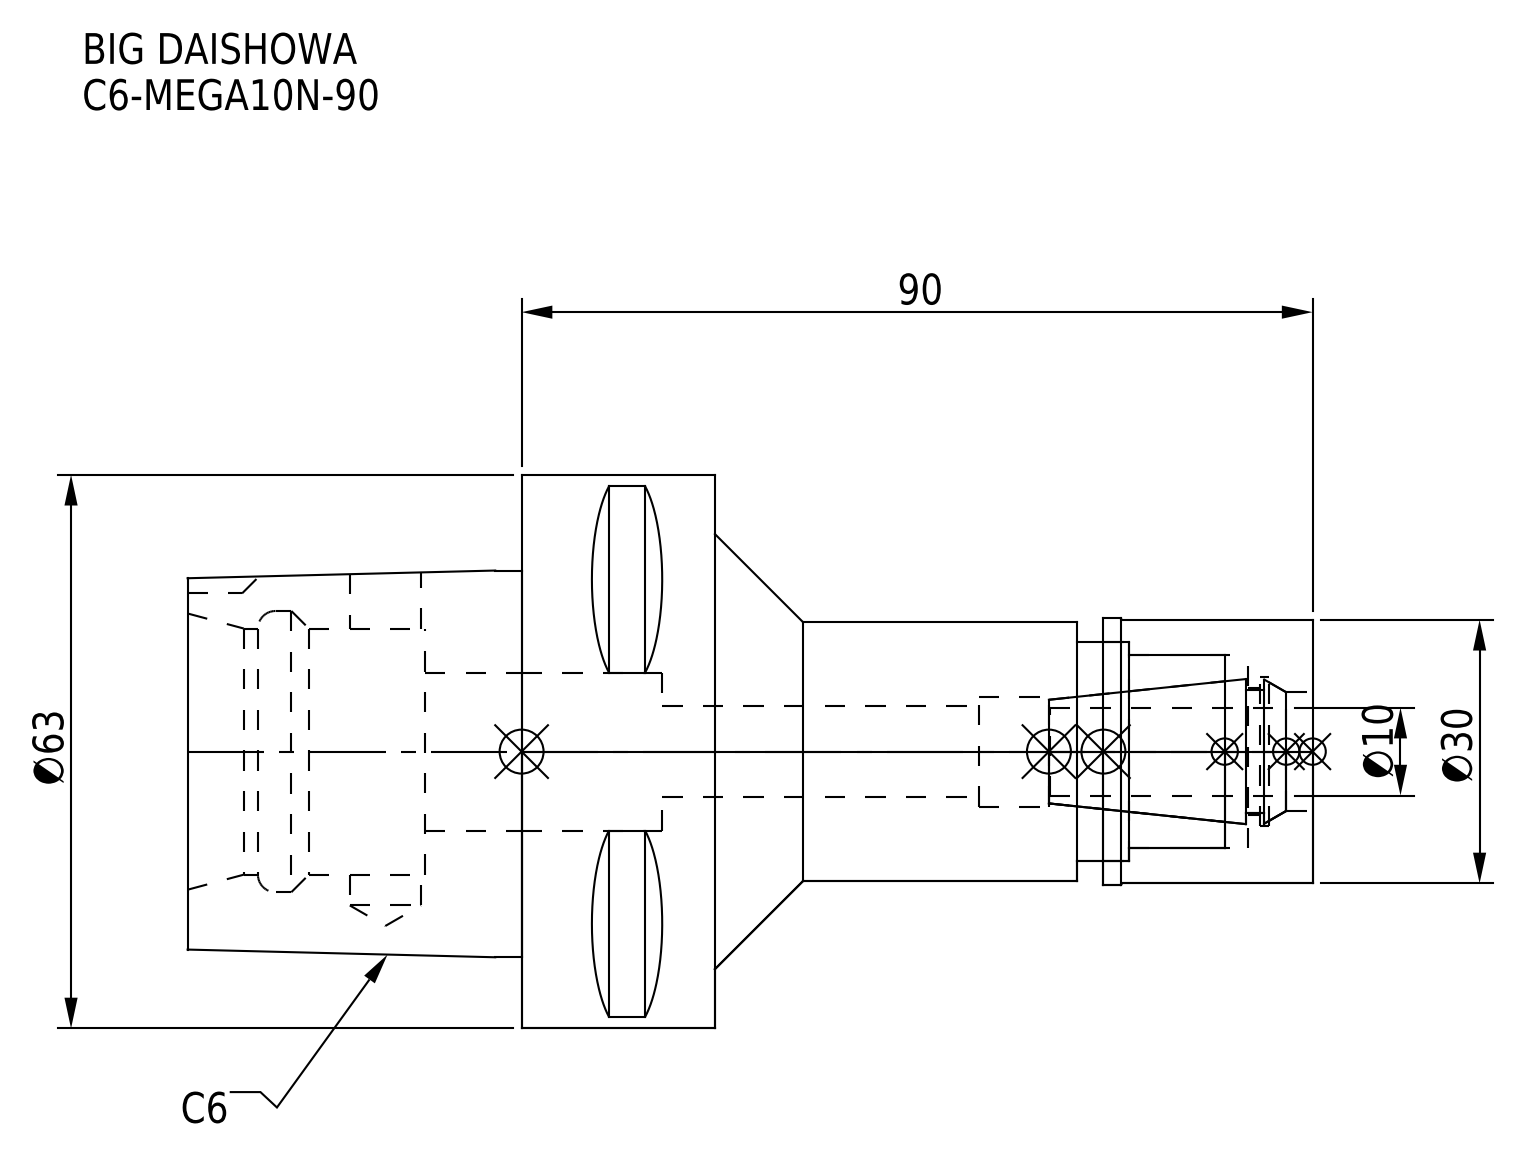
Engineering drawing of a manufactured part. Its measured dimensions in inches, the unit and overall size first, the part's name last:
Units: inches
Overall size (bounding box): 5.039 × 2.48 × 2.48
Round holes (diameter × count): ⌀0.319 ×1, ⌀0.409 ×1, ⌀0.492 ×1, ⌀0.531 ×1, ⌀0.571 ×1, ⌀0.669 ×1, ⌀0.709 ×1, ⌀0.866 ×1, ⌀0.984 ×1, ⌀1.102 ×1, ⌀1.26 ×1
Round bosses / shafts (diameter × count): ⌀2.48 ×1, ⌀1.193 ×1, ⌀1.181 ×1, ⌀1.161 ×1
Partial cylindrical surfaces — rounded edges, fillets, slot ends (radius × count): R0.197 ×1
Main face-to-face distances: 0.866, 2.677, 3.543, 1.496, 1.063, 2.362, 5.039, 1.299, 3.976, 0.433
Volume: 8.507 in³ · Surface area: 49.4 in²
Bodies: 2 solids, 95 faces (38 planar, 39 cylindrical, 18 other)
Part name (STEP PRODUCT): C6-MEGA10N-90; C6-MEGA10N-90-100-FreeParts; DXF_TEMP_ASSY_ASM_4_ASM.stp; MGN10_1.stp (+3 more)
STEP written by: SolidWorks 2019 (CONFIG_CONTROL_DESIGN)
